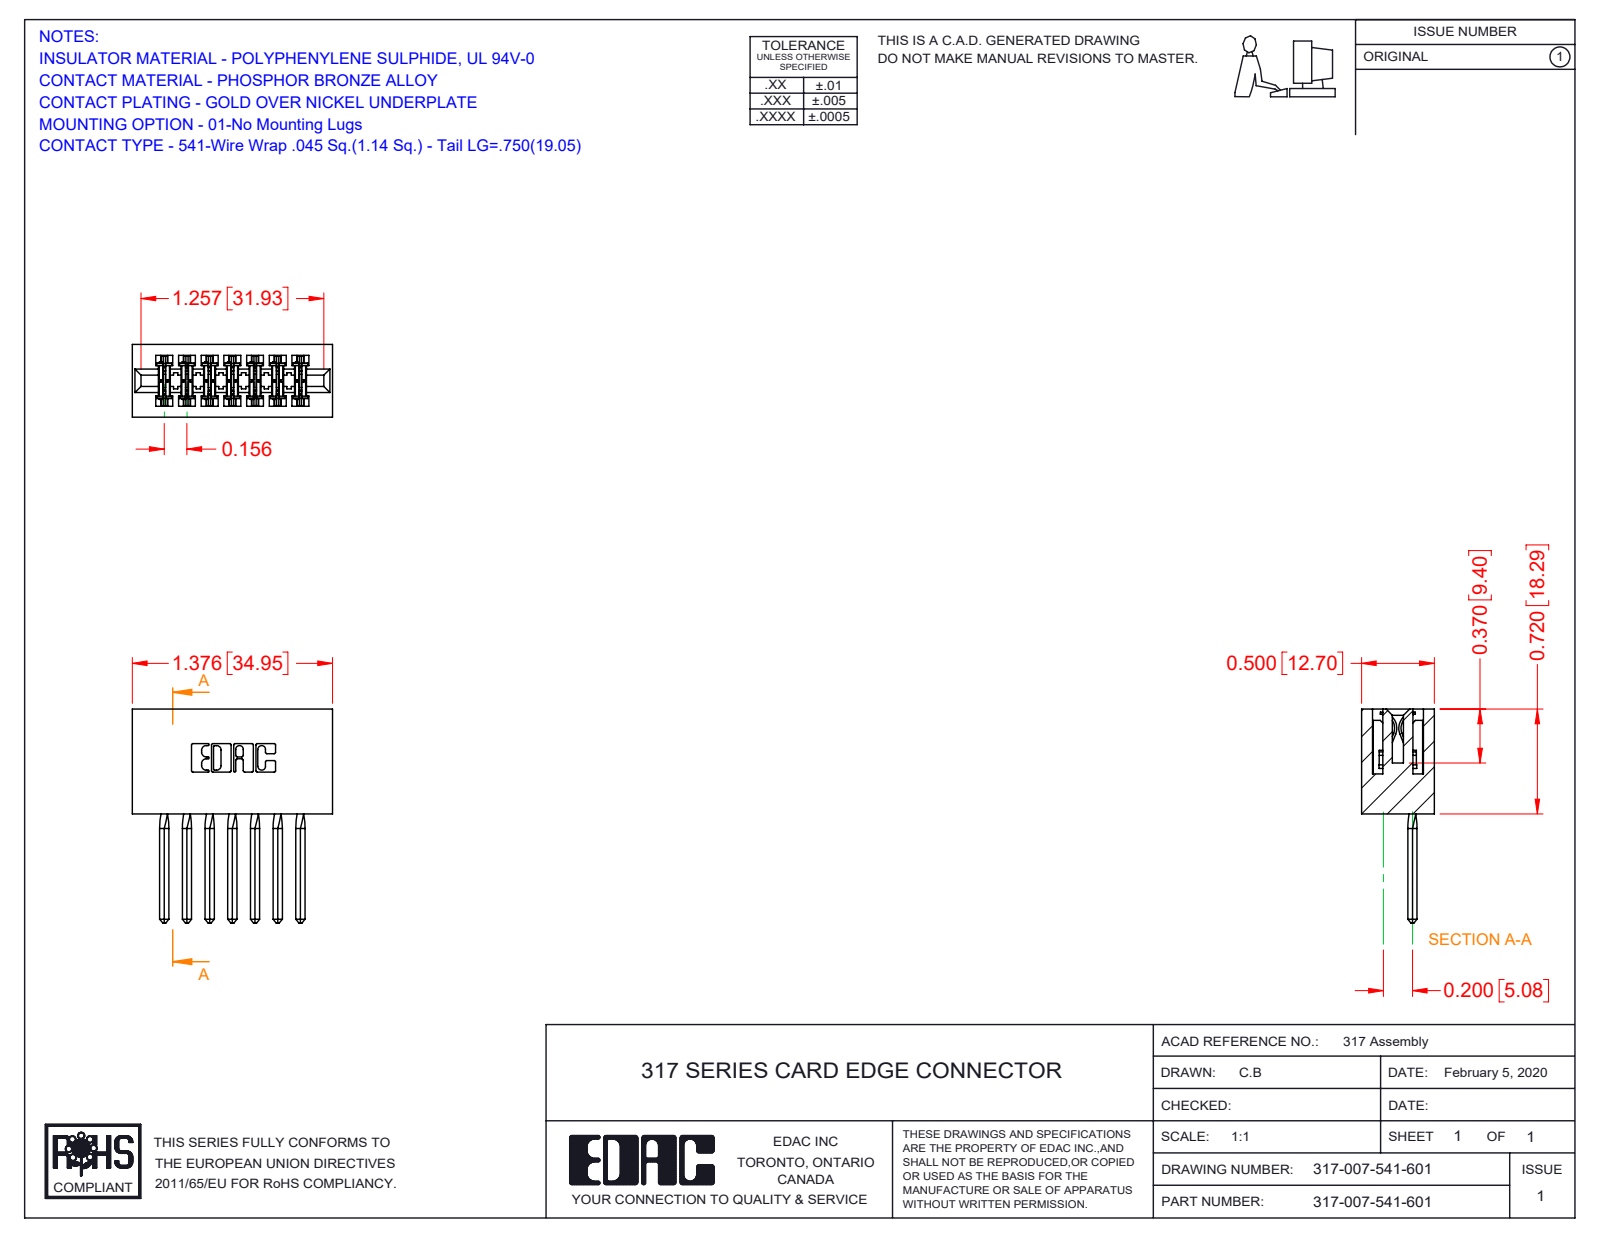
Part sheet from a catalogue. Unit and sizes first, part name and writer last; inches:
Units: inches
Overall size (bounding box): 1.47 × 1.376 × 0.5
Partial cylindrical surfaces — rounded edges, fillets, slot ends (radius × count): R0.01 ×22, R0.015 ×14, R0.007 ×6, R0.031 ×6, R0.026 ×3, R0.095 ×2, R0.1 ×2, R0.11 ×2
Main face-to-face distances: 0.5, 0.075, 0.425, 0.11, 0.156, 0.065, 0.22, 0.116, 0.312, 0.136
Volume: 0.384 in³ · Surface area: 12.28 in²
Bodies: 8 solids, 1154 faces (918 planar, 208 cylindrical, 28 other)
Part name (STEP PRODUCT): 317 Part_Lugless; 317-007-541-601; 317-290-002_541
STEP written by: SolidWorks 2016 (CONFIG_CONTROL_DESIGN)
